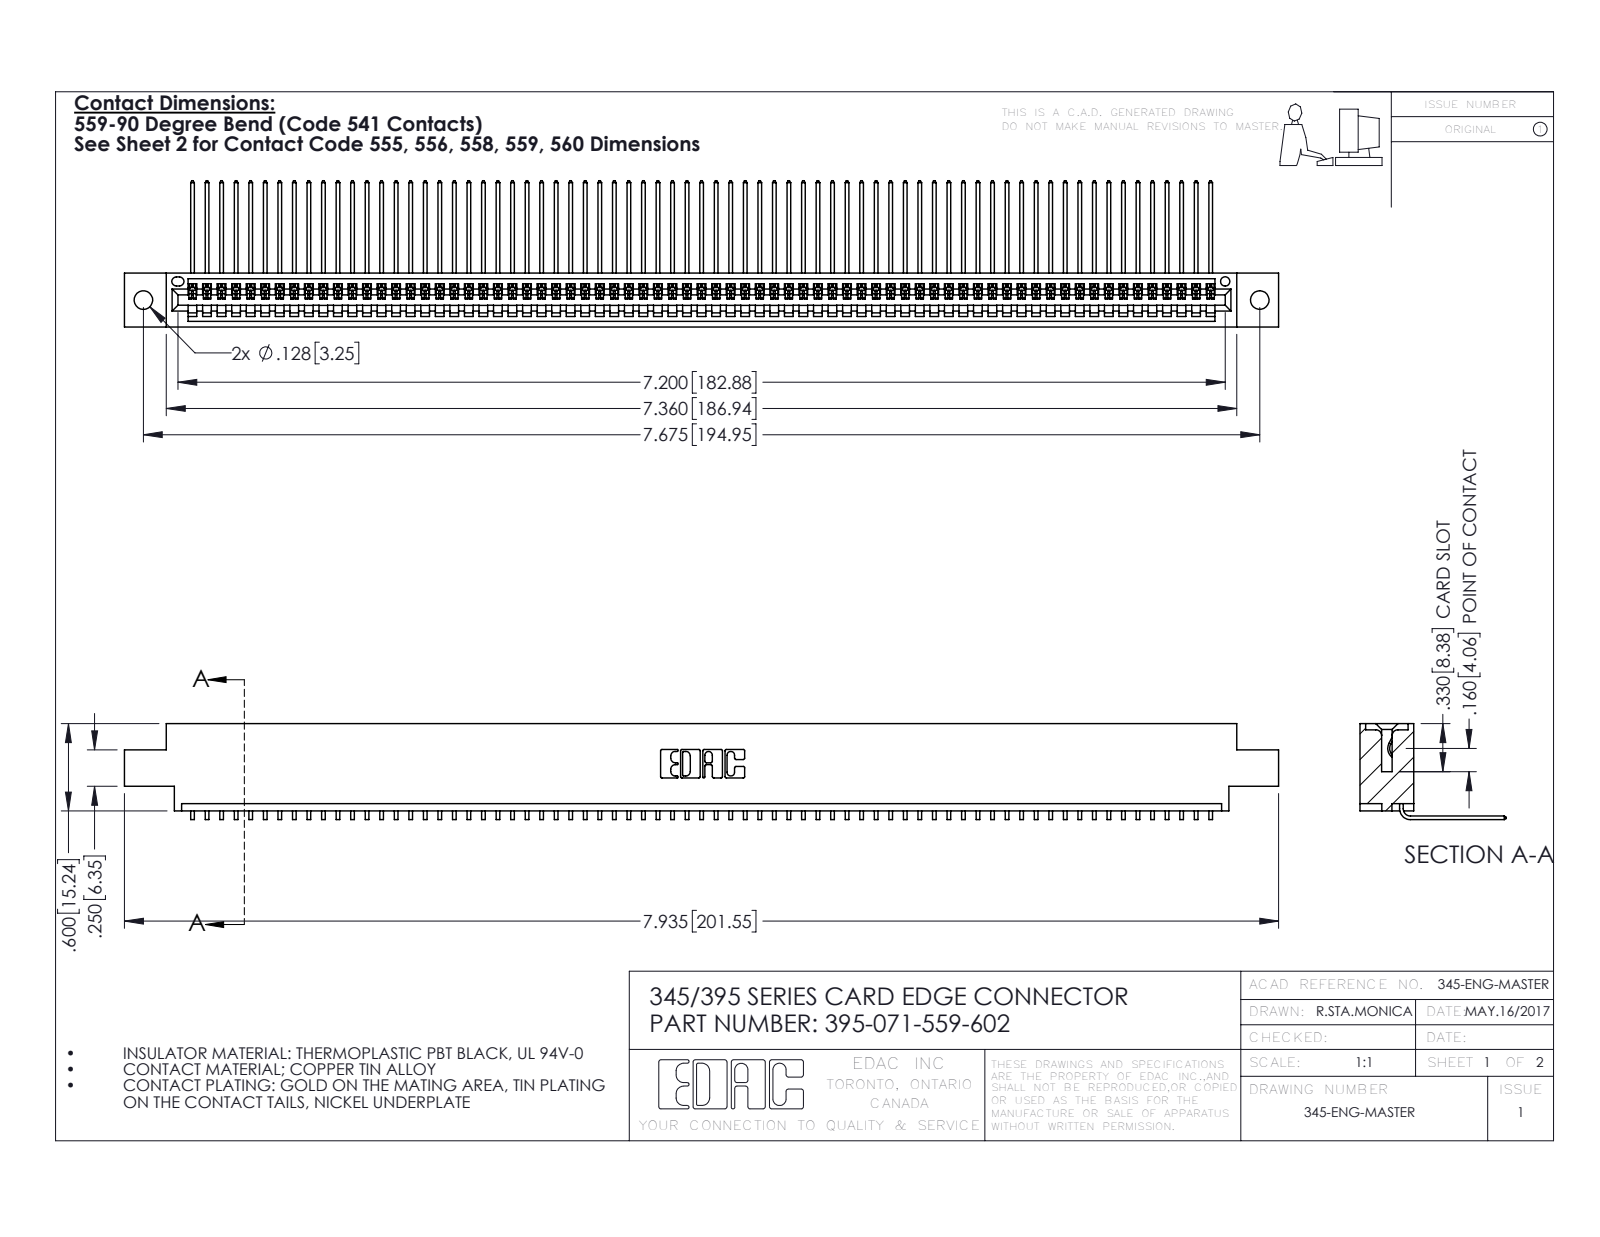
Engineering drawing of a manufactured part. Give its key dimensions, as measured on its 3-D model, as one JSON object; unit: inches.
{"part_name": "345 Part_0.170 Offset - 0.128 Dia; 345-292-001_558 559 Tail - 1; 395-071-559-602", "step_written_by": "SolidWorks 2016 (CONFIG_CONTROL_DESIGN)", "units": "inches", "bodies": {"solids": 72, "faces": 4390, "planar": 3066, "cylindrical": 1324, "other": 0}, "overall_size": [7.935, 1.005, 0.659], "volume_in3": 1.188, "surface_area_in2": 42.64, "round_holes": [[0.128, 2], [0.064, 1]], "partial_cylinders_radius": [[0.006, 142], [0.01, 22], [0.007, 6], [0.031, 6], [0.026, 3], [0.031, 2], [0.04, 2], [0.014, 1]], "face_to_face_distances": [0.072, 0.298, 0.37, 0.2, 0.098, 0.272, 0.025, 0.225, 0.175, 0.149], "hole_center_spacings": [0.27, 7.439, 7.675]}
